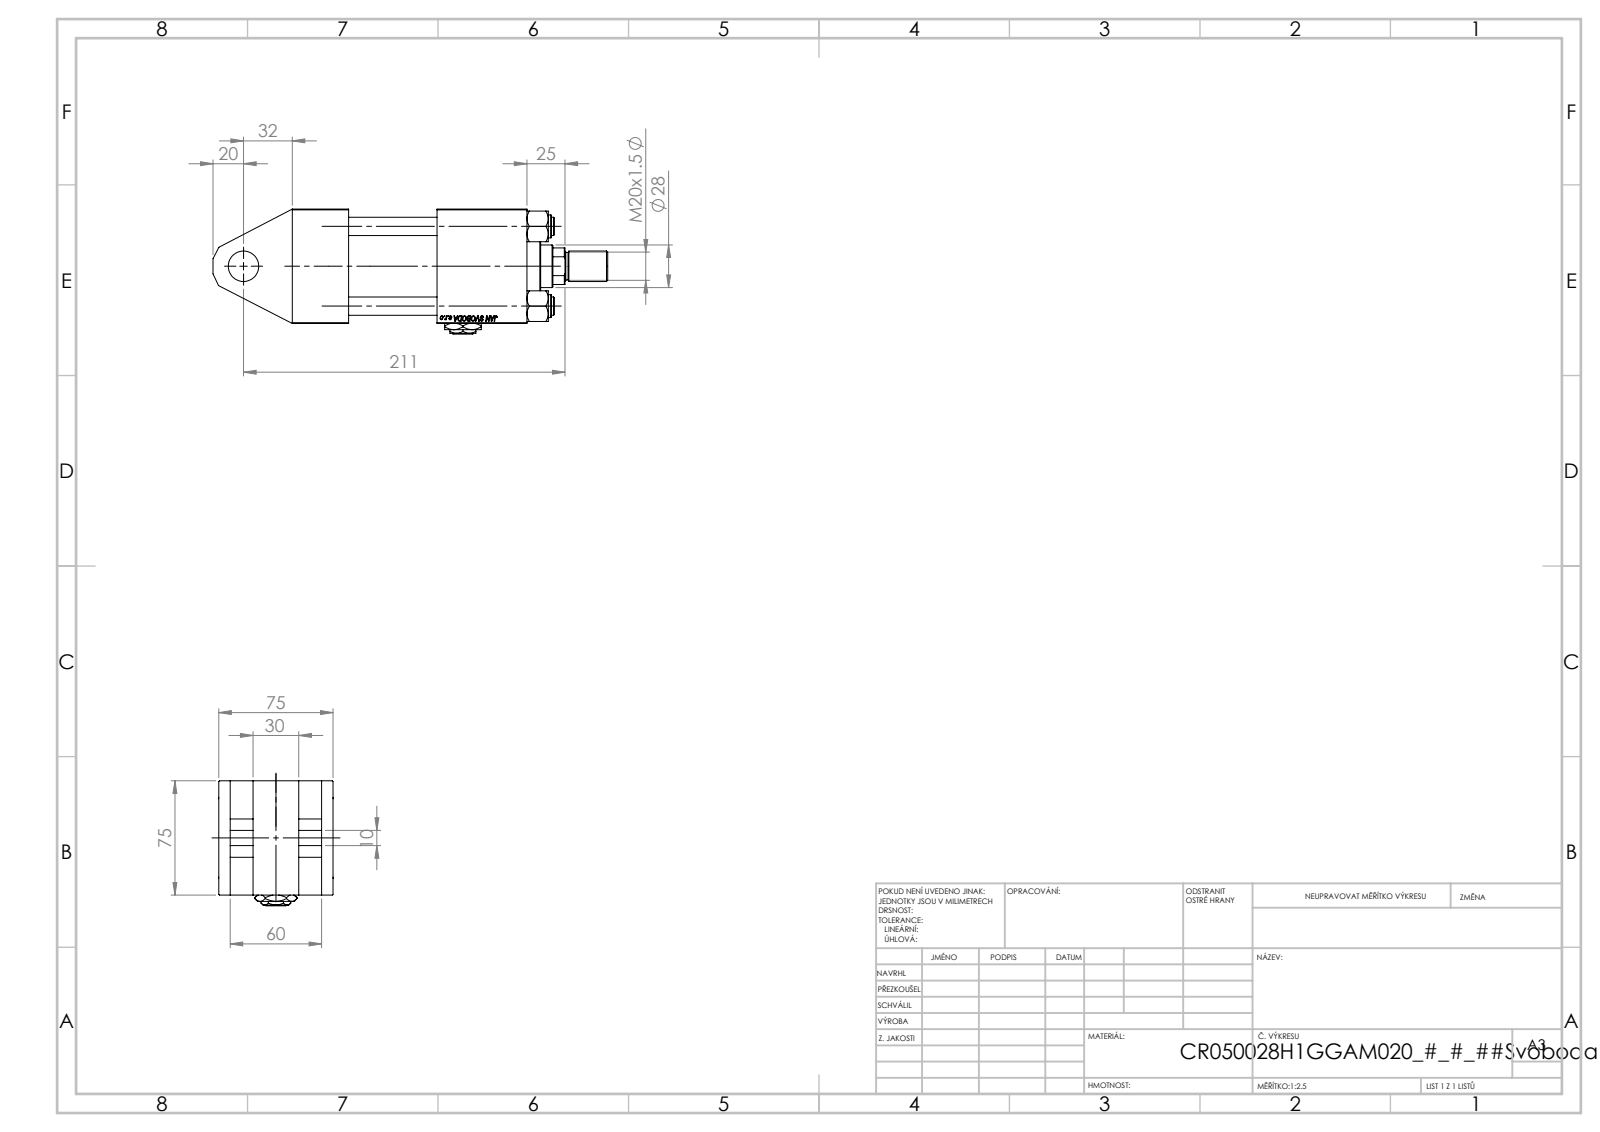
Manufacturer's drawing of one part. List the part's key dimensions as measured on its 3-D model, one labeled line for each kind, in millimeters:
Part name (STEP PRODUCT): V215_VC_A; Zatka_pro_OIL_PORT; ROD_END_AH; V215CR_TYCINKA_H (+3 more)
STEP written by: SolidWorks 2019 (CONFIG_CONTROL_DESIGN)
Units: millimetres
Bodies: 13 solids, 1189 faces (545 planar, 90 cylindrical, 554 other)
Overall size (bounding box): 259 × 82 × 75.54
Volume: 751 603 mm³ · Surface area: 170 918 mm²
Round holes (diameter × count): ⌀12 ×4, ⌀7 ×2, ⌀20.96 ×2, ⌀30 ×2, ⌀18.5 ×1, ⌀20 ×1, ⌀28 ×1, ⌀31 ×1, ⌀41 ×1, ⌀50 ×1, ⌀53 ×1
Round bosses / shafts (diameter × count): ⌀15 ×4, ⌀56 ×1, ⌀42 ×1, ⌀20 ×1, ⌀18 ×1
Partial cylindrical surfaces — rounded edges, fillets, slot ends (radius × count): R13.5 ×1
Main face-to-face distances: 75, 67.5, 7.5, 22.5, 52.5, 15, 45, 117, 37, 95
Hole centre spacings: 36.98, 52.3, 73.96, 93.5
